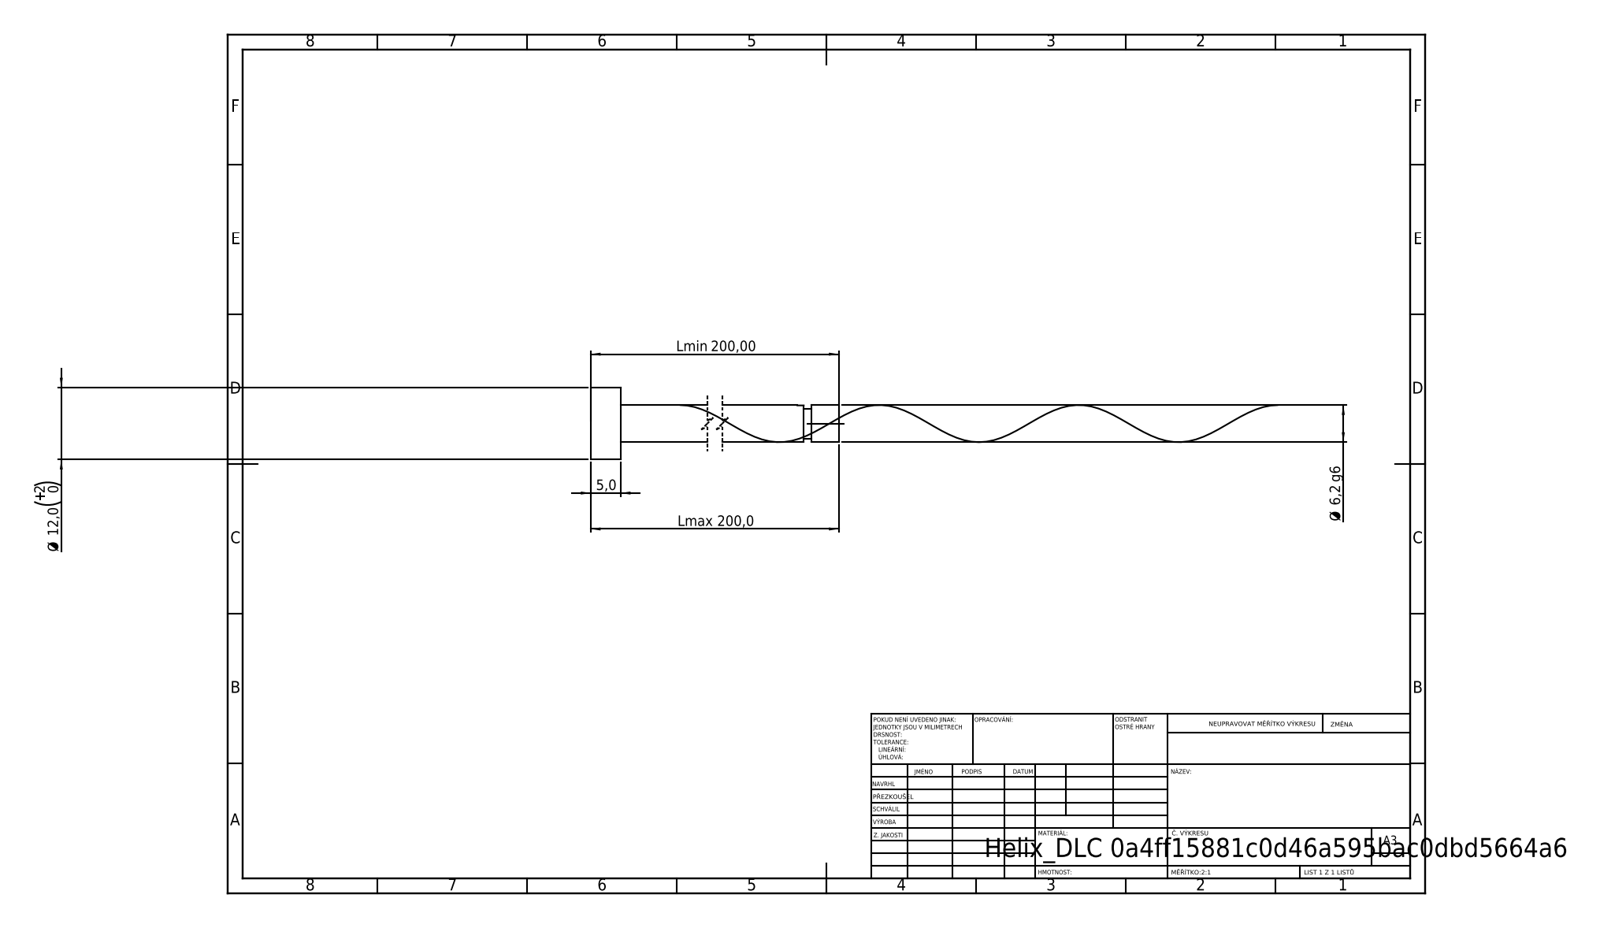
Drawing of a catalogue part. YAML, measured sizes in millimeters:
step_written_by: "SolidWorks 2019 (CONFIG_CONTROL_DESIGN)"
units: millimeters
bodies: {solids: 1, faces: 21, planar: 6, cylindrical: 14, other: 1}
overall_size: [200, 12, 12]
volume: 6381
surface_area: 4302
round_bosses_or_shafts:
  - {diameter: 12, count: 1}
  - {diameter: 6.2, count: 1}
  - {diameter: 4.96, count: 1}
face_to_face_distances: [5, 200, 195, 195.38, 190.38, 4.62, 194.14, 189.14, 1.24, 5.86]
